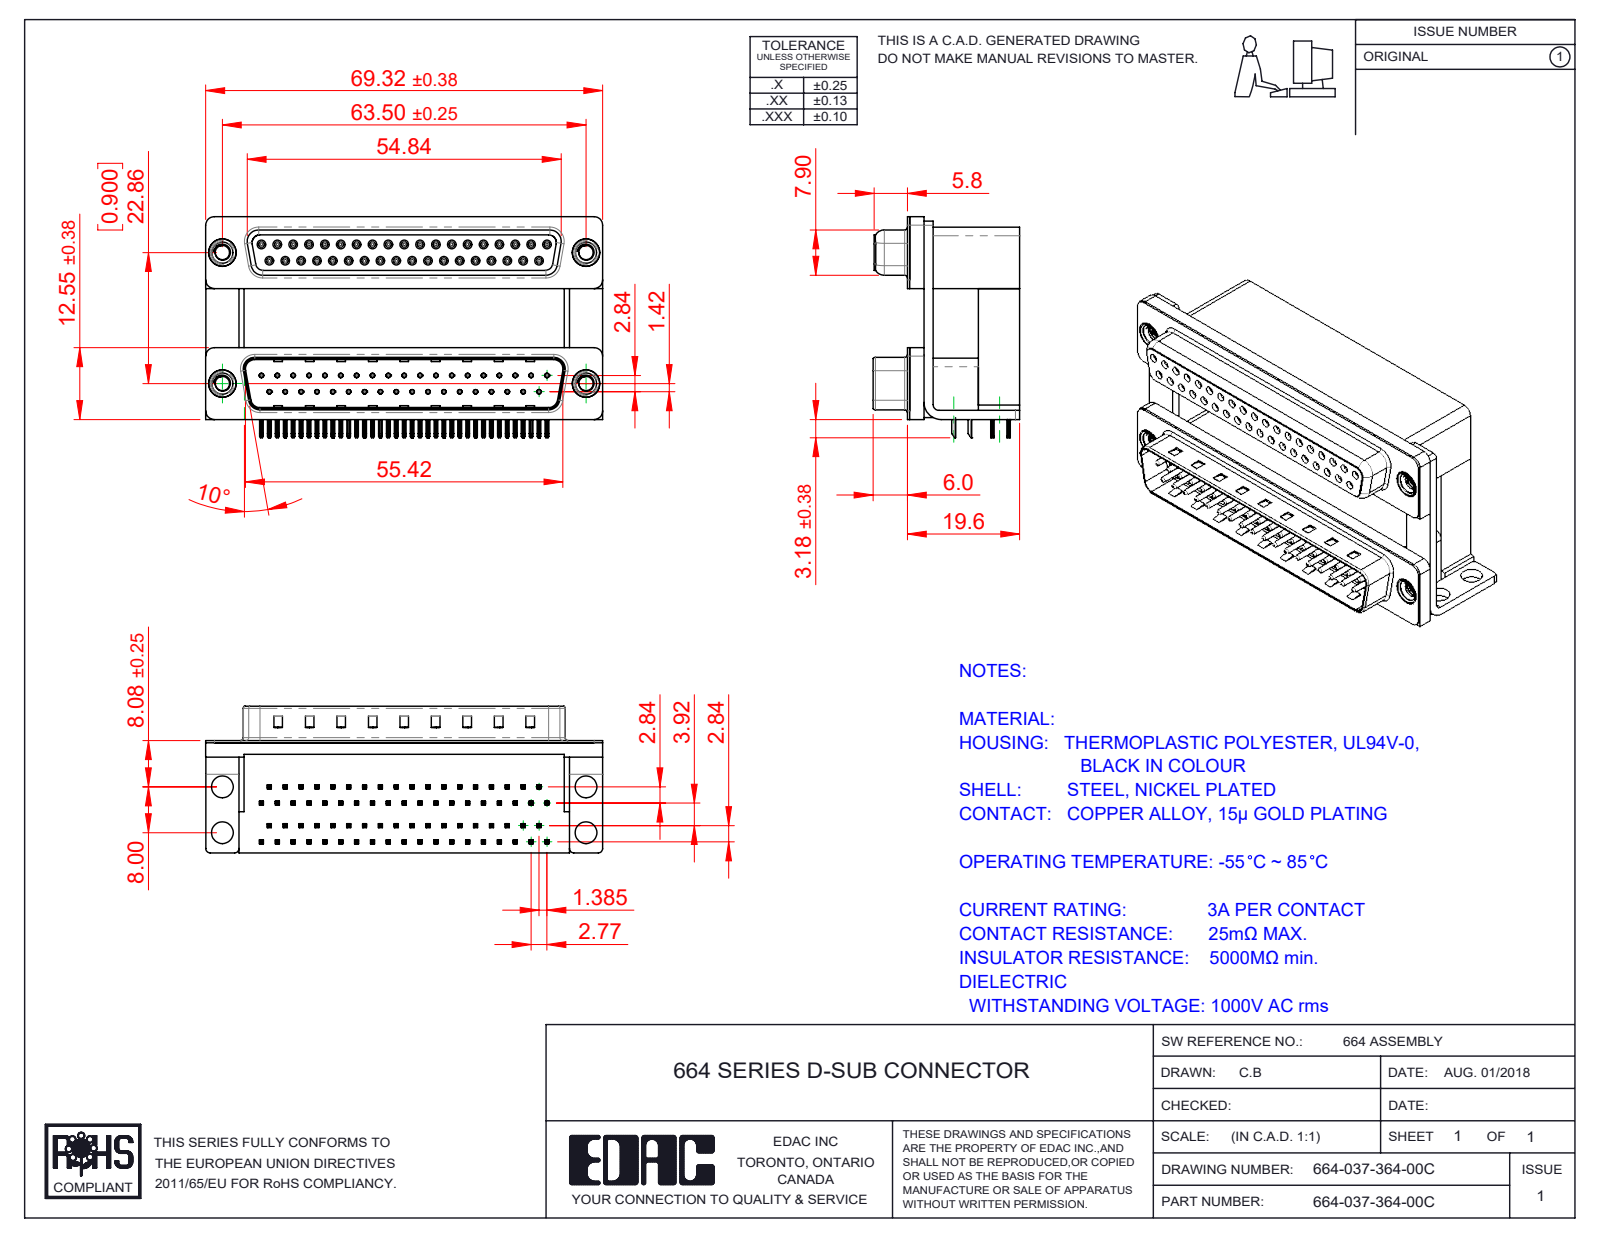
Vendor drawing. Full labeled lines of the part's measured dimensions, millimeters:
Part name (STEP PRODUCT): 664 Contact Bottom Upper_H; 664 Housing Upper_37 Contacts H; 664 Contact Top Lower; 664 Shell Plug_37 Contacts (+8 more)
STEP written by: SolidWorks 2020 (CONFIG_CONTROL_DESIGN)
Units: millimetres
Bodies: 85 solids, 8949 faces (4741 planar, 2185 cylindrical, 2023 other)
Overall size (bounding box): 69.32 × 38.59 × 25.6
Volume: 32 651 mm³ · Surface area: 34 047 mm²
Round holes (diameter × count): ⌀0.8 ×74, ⌀0.35 ×37, ⌀0.9 ×37, ⌀2.5 ×4, ⌀3.5 ×4, ⌀3.8 ×4, ⌀4 ×4, ⌀4.8 ×4, ⌀5 ×4
Round bosses / shafts (diameter × count): ⌀1.2 ×37, ⌀0.75 ×37, ⌀4.9 ×4, ⌀4.75 ×4, ⌀3.9 ×4
Partial cylindrical surfaces — rounded edges, fillets, slot ends (radius × count): R0.1 ×296, R0.15 ×148, R0.25 ×148, R0.12 ×74, R0.35 ×74, R0.34 ×37, R0.28 ×18, R1.5 ×13
Main face-to-face distances: 19.2, 0.4, 12, 7.2, 2.19, 2.84, 0.65, 22.5, 10.69, 0.45
Hole centre spacings: 2.77, 5.54, 3.16, 8.31, 11.08, 13.85, 16.62, 19.39
